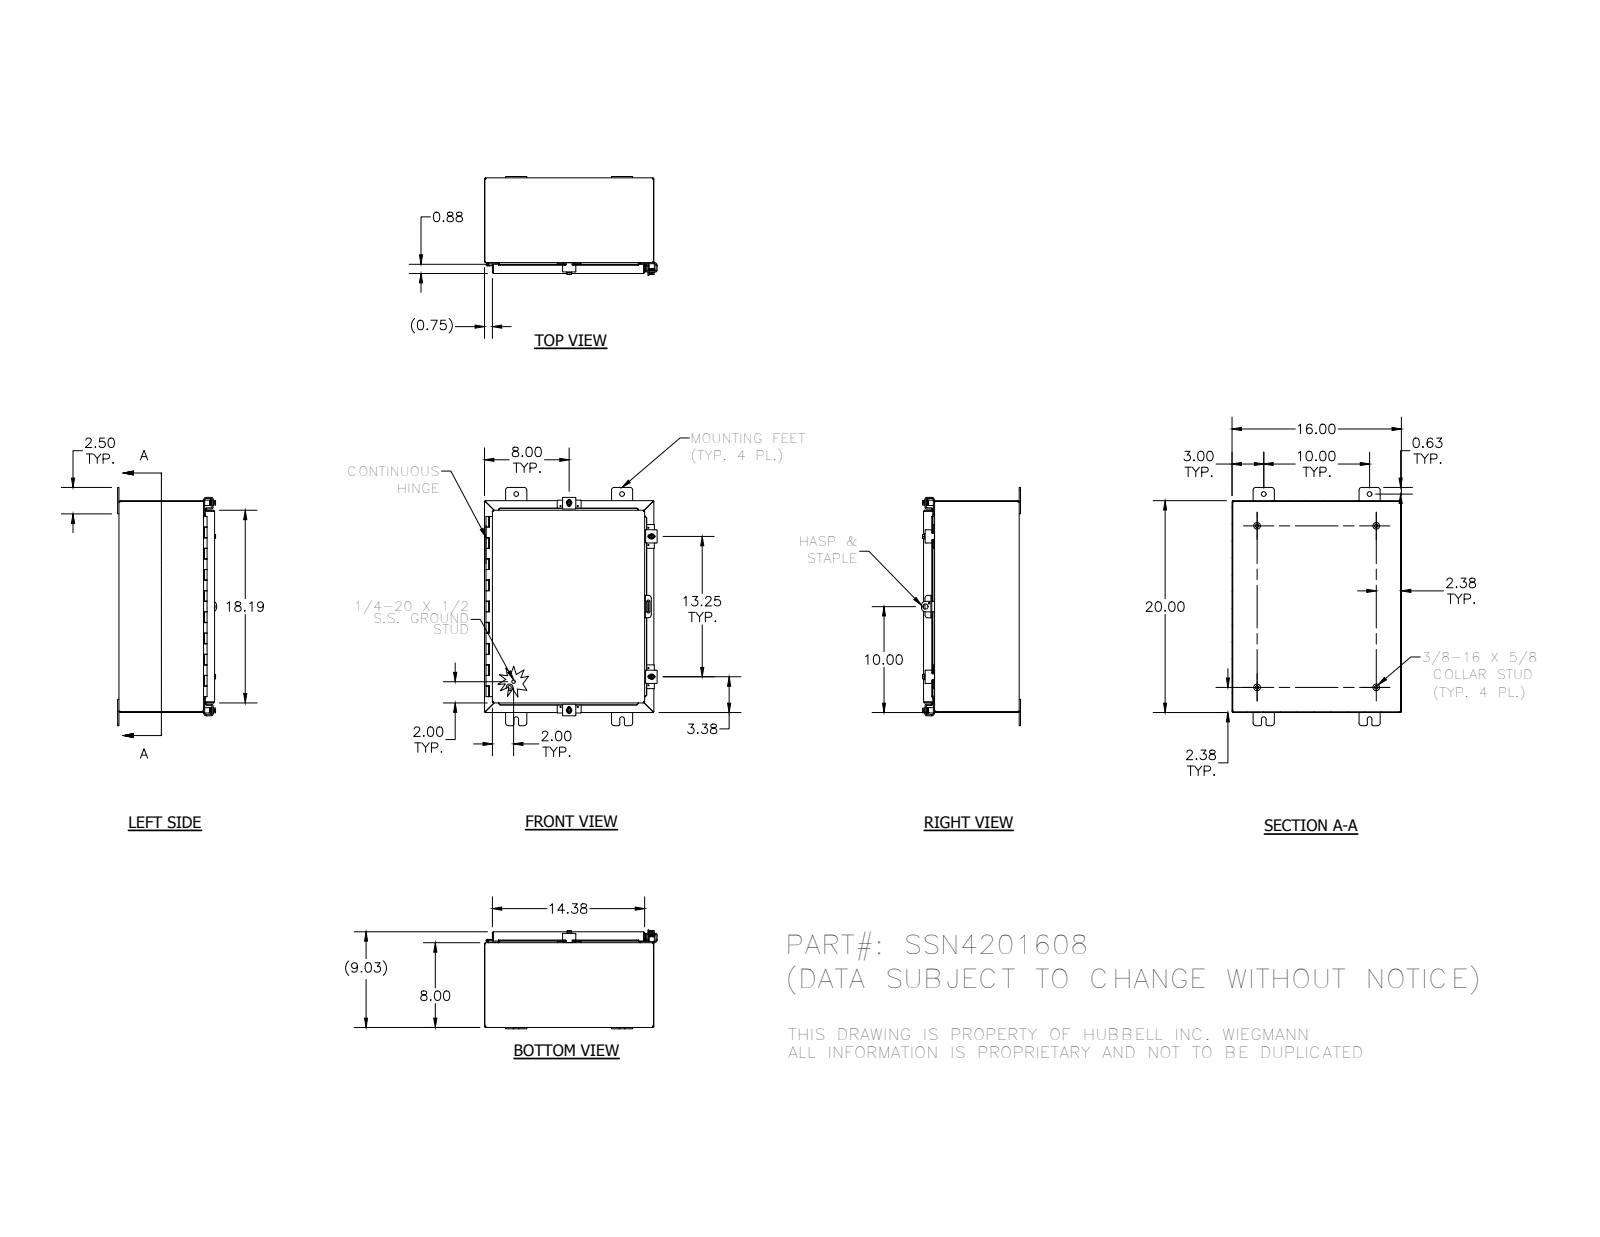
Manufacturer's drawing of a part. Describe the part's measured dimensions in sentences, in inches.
The part is named "30818_1; 30824-1_1; HFW30825-3_1; 328137L_1 (+8 more)". Its 3-D file was written by "SolidWorks 2014 (AUTOMOTIVE_DESIGN)". It is 37 solids with 1444 faces: 567 planar, 632 cylindrical and 245 other. Overall it measures 22.5 by 16.311 by 9.355 inches. Its volume is 114.6 cubic inches and its surface area 2 993 square inches. Round holes: 8 of diameter 0.11, 4 of diameter 0.211, 4 of diameter 0.281, 4 of diameter 0.3, 4 of diameter 0.438, 1 of diameter 0.125, 1 of diameter 0.156, 1 of diameter 0.5. Round bosses or shafts: 6 of diameter 0.25, 4 of diameter 0.625, 4 of diameter 0.52, 4 of diameter 0.5, 4 of diameter 0.35, 4 of diameter 0.33, 2 of diameter 0.115, 1 of diameter 0.337. Partial cylindrical surfaces (rounded edges, fillets, slot ends): 49 of radius 0.03, 33 of radius 0.125, 29 of radius 0.25, 23 of radius 0.031, 23 of radius 0.105, 11 of radius 0.062, 8 of radius 0.07, 8 of radius 0.141. The main face-to-face distances are 0.074, 8.959, 15.926, 8.885, 9.033, 19.926, 7.926, 1.033, 15.852, 16. The hole center spacings are 0.876, 19.306, 13.25, 0.876, 1.625, 1.625, 4.189, 4.341.
